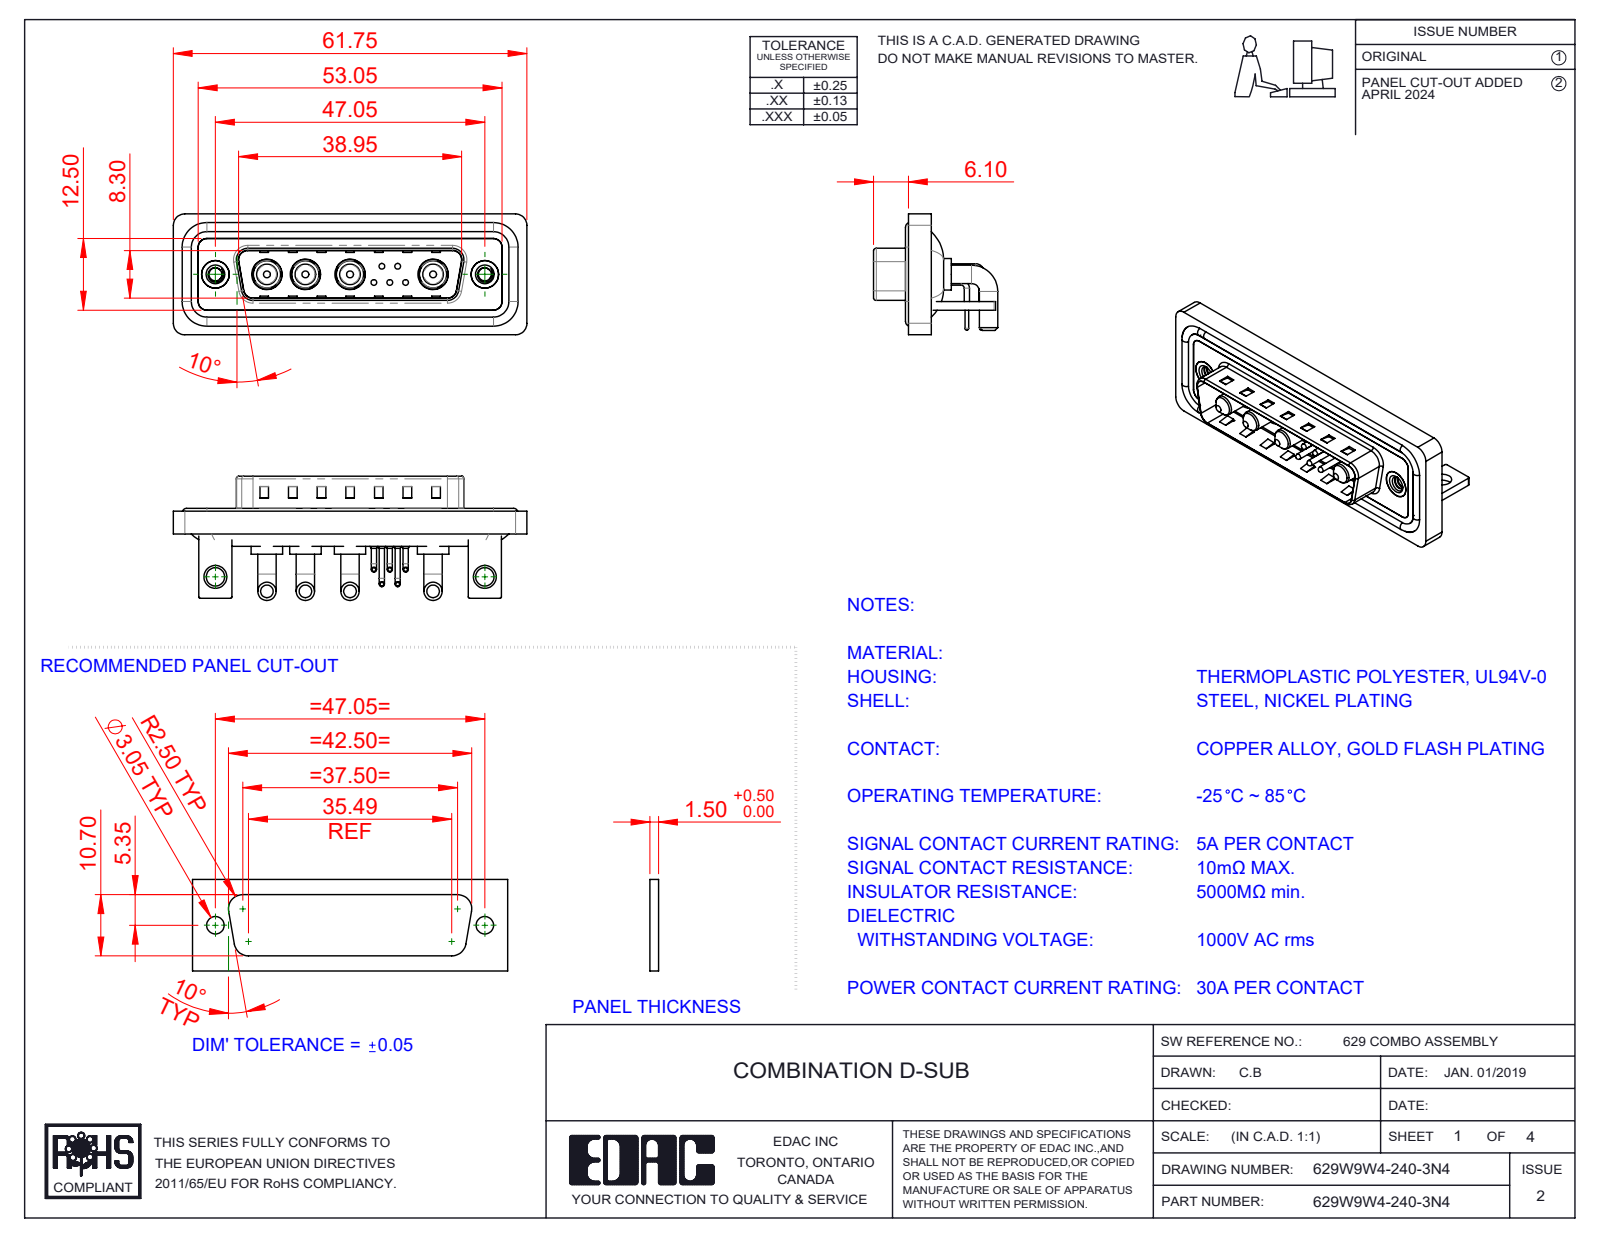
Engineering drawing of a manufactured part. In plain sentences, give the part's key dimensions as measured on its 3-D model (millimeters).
The part is named "629Combo Waterproof Housing_25 Contacts; 629Combo Threaded Rivet_3; Power Pin_30A RA; 629W9W4-140-3N4 (+6 more)". Its 3-D file was written by "SolidWorks 2023 (CONFIG_CONTROL_DESIGN)". It is 22 solids with 1245 faces: 589 planar, 470 cylindrical and 186 other. Overall it measures 61.75 by 21.7 by 21.1 millimeters. Its volume is 8 094 cubic millimeters and its surface area 13 037 square millimeters. Round holes: 5 of diameter 0.75, 5 of diameter 1.6, 5 of diameter 2, 4 of diameter 4.85, 4 of diameter 5.3, 2 of diameter 2.26, 2 of diameter 3.2, 2 of diameter 4, 2 of diameter 4.8, 2 of diameter 5. Round bosses or shafts: 10 of diameter 0.9, 8 of diameter 3.2, 5 of diameter 1.5, 5 of diameter 1, 5 of diameter 0.65, 4 of diameter 5.5, 4 of diameter 5.2, 4 of diameter 4.75. Partial cylindrical surfaces (rounded edges, fillets, slot ends): 19 of radius 2, 18 of radius 1.5, 16 of radius 0.25, 9 of radius 0.5, 8 of radius 1.6, 5 of radius 1.01, 4 of radius 0.6, 4 of radius 0.65. The main face-to-face distances are 0.4, 1.5, 0.8, 2.9, 2.1, 1.1, 3.7, 4.1, 4.5, 1.6. The hole center spacings are 3.16, 2.77, 5.04, 14.5, 47.05, 2.78, 4.4, 4.41.
